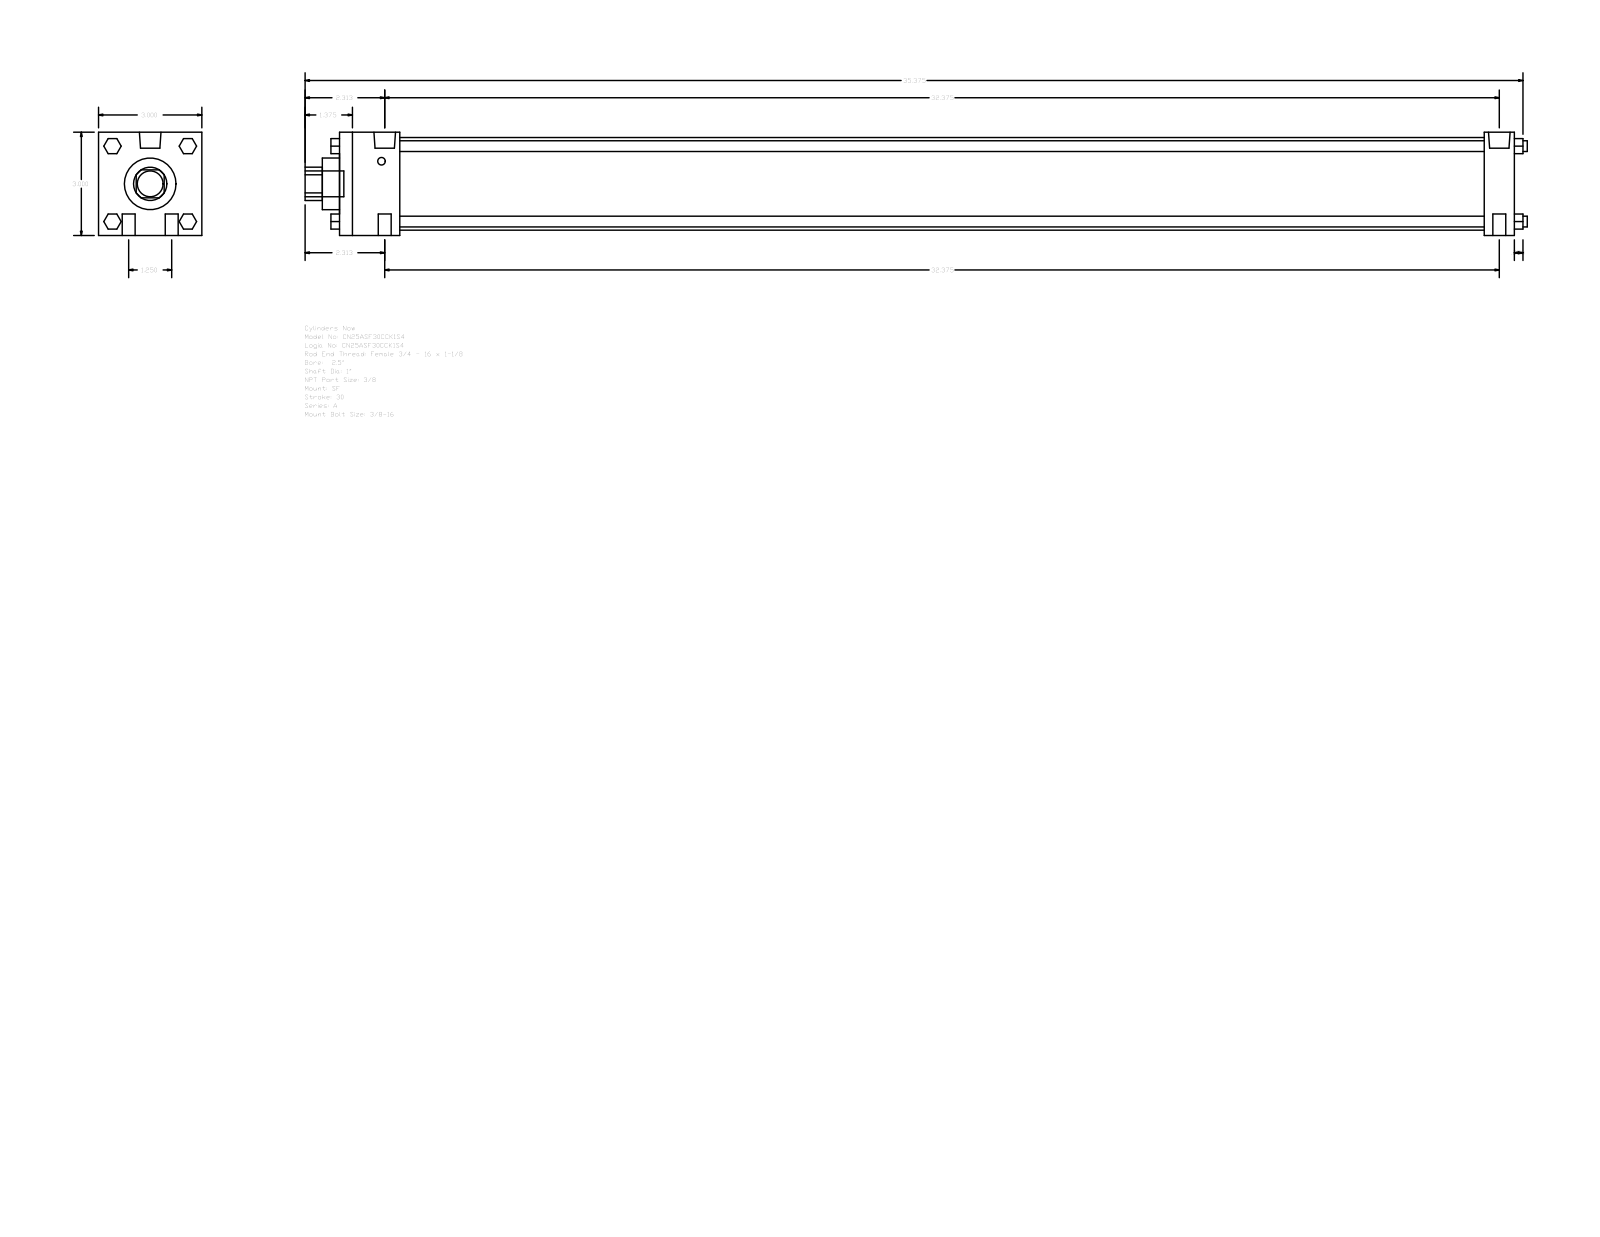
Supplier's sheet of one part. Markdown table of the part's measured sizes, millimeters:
| quantity | value |
| --- | --- |
| part name | A_SF__0250_1 |
| STEP written by | GSSL Pune (CONFIG_CONTROL_DESIGN) |
| units | millimeters |
| bodies | 0 solids, 124 faces (94 planar, 30 cylindrical, 0 other) |
| overall size | 901.7 × 76.2 × 76.2 |
| round holes (diameter × count) | 25.4 × 1, 38.1 × 1, 68.33 × 1 |
| round bosses / shafts (diameter × count) | 9.53 × 4, 7.94 × 4, 15.93 × 2, 5.56 × 2, 19.05 × 1 |
| partial cylindrical surfaces (radius × count) | 12.29 × 1 |
| main face-to-face distances | 76.2, 866.77, 844.55, 22.22, 44.45, 800.1, 822.32, 12.7, 879.47, 6.35 |
